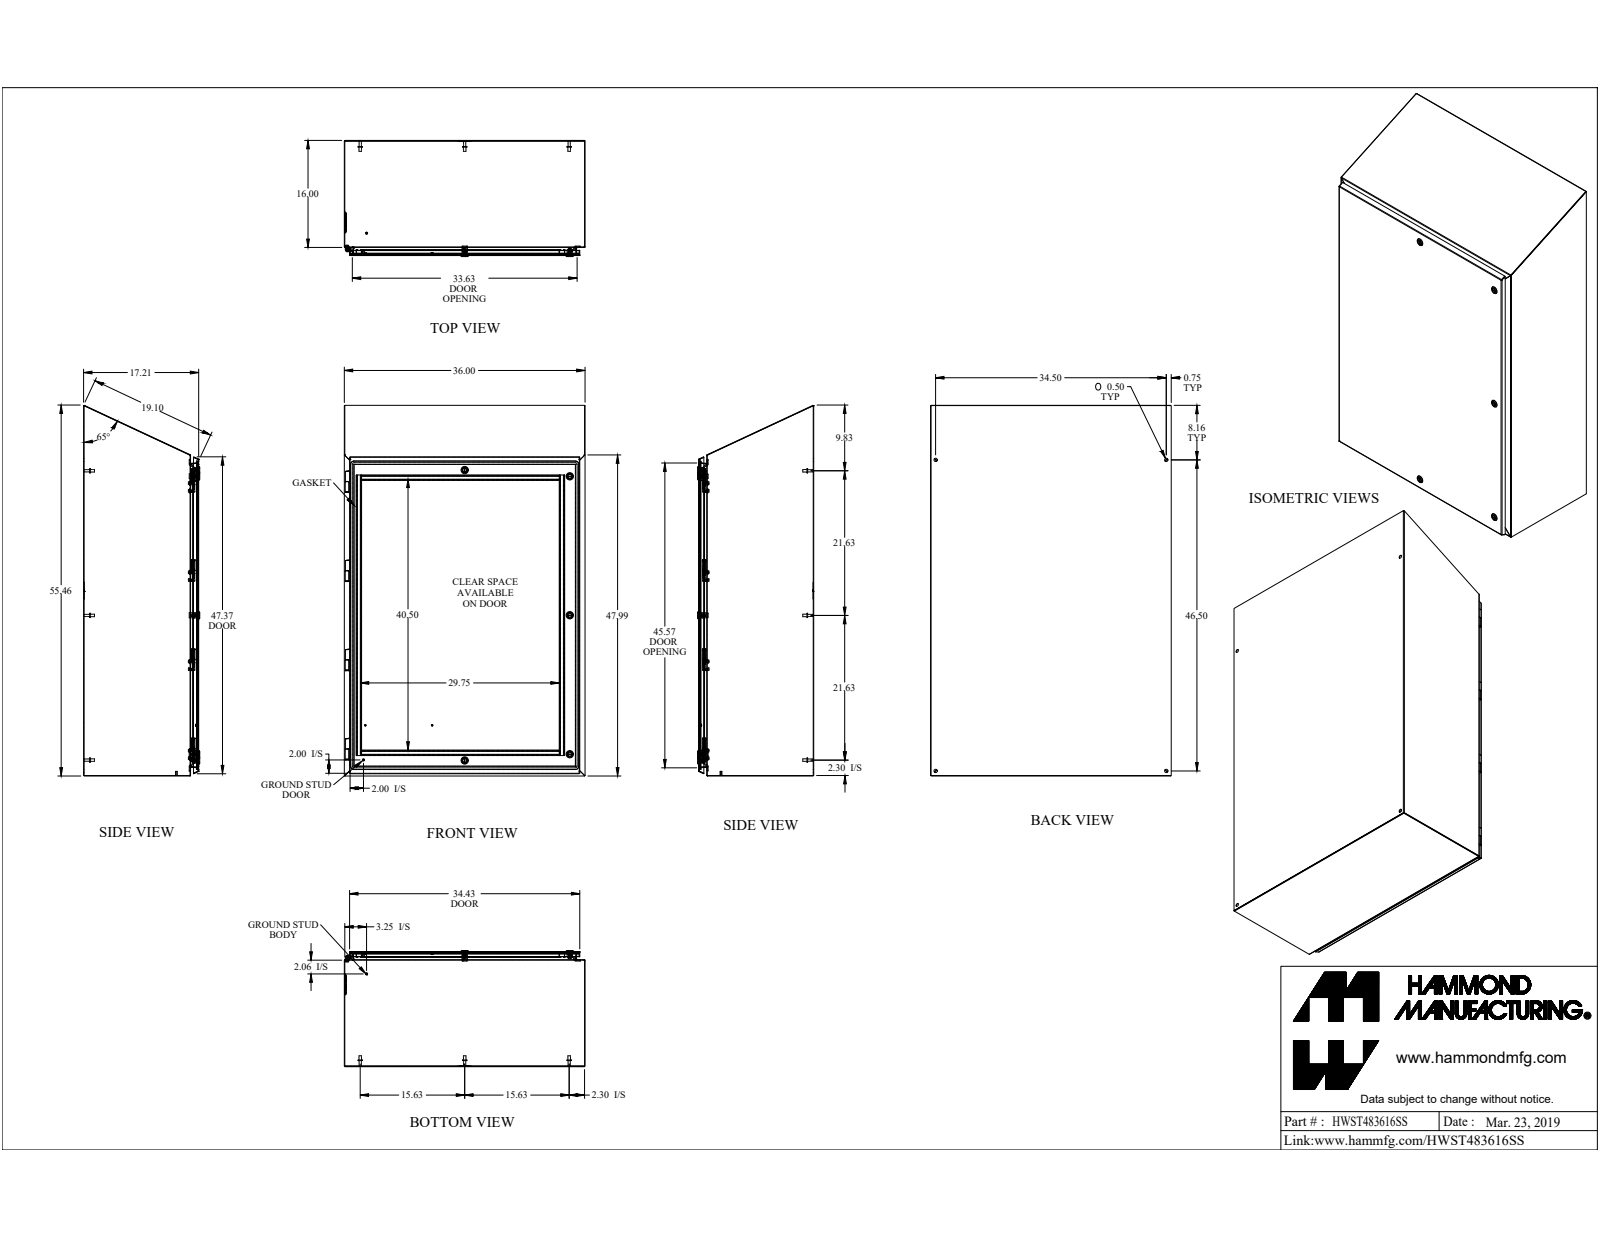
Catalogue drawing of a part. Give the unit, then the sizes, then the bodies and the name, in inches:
Units: inches
Overall size (bounding box): 55.409 × 36 × 17.37
Round holes (diameter × count): ⌀0.194 ×16, ⌀0.24 ×16, ⌀0.5 ×9, ⌀0.275 ×8, ⌀0.197 ×5, ⌀0.387 ×5, ⌀0.63 ×5, ⌀0.768 ×5, ⌀0.13 ×2, ⌀0.24 ×1, ⌀3.5 ×1
Round bosses / shafts (diameter × count): ⌀0.226 ×16, ⌀0.625 ×12, ⌀0.65 ×8, ⌀0.375 ×8, ⌀0.332 ×8, ⌀0.236 ×6, ⌀1.1 ×5, ⌀0.785 ×4
Partial cylindrical surfaces — rounded edges, fillets, slot ends (radius × count): R0.039 ×32, R0.125 ×26, R0.043 ×24, R0.25 ×24, R0.012 ×20, R0.036 ×17, R0.108 ×17, R0.03 ×16
Main face-to-face distances: 0.072, 0.072, 17.066, 17.138, 17.138, 17.21, 35.856, 35.928, 35.928, 36
Hole centre spacings: 13.324, 1.142, 13.325, 26.649, 1.142, 12.183, 26.649, 13.326
Volume: 547.1 in³ · Surface area: 15 377 in²
Bodies: 86 solids, 1971 faces (1216 planar, 539 cylindrical, 216 other)
Part name (STEP PRODUCT): HWST483616S16
STEP written by: SolidWorks 2019 (AUTOMOTIVE_DESIGN)
